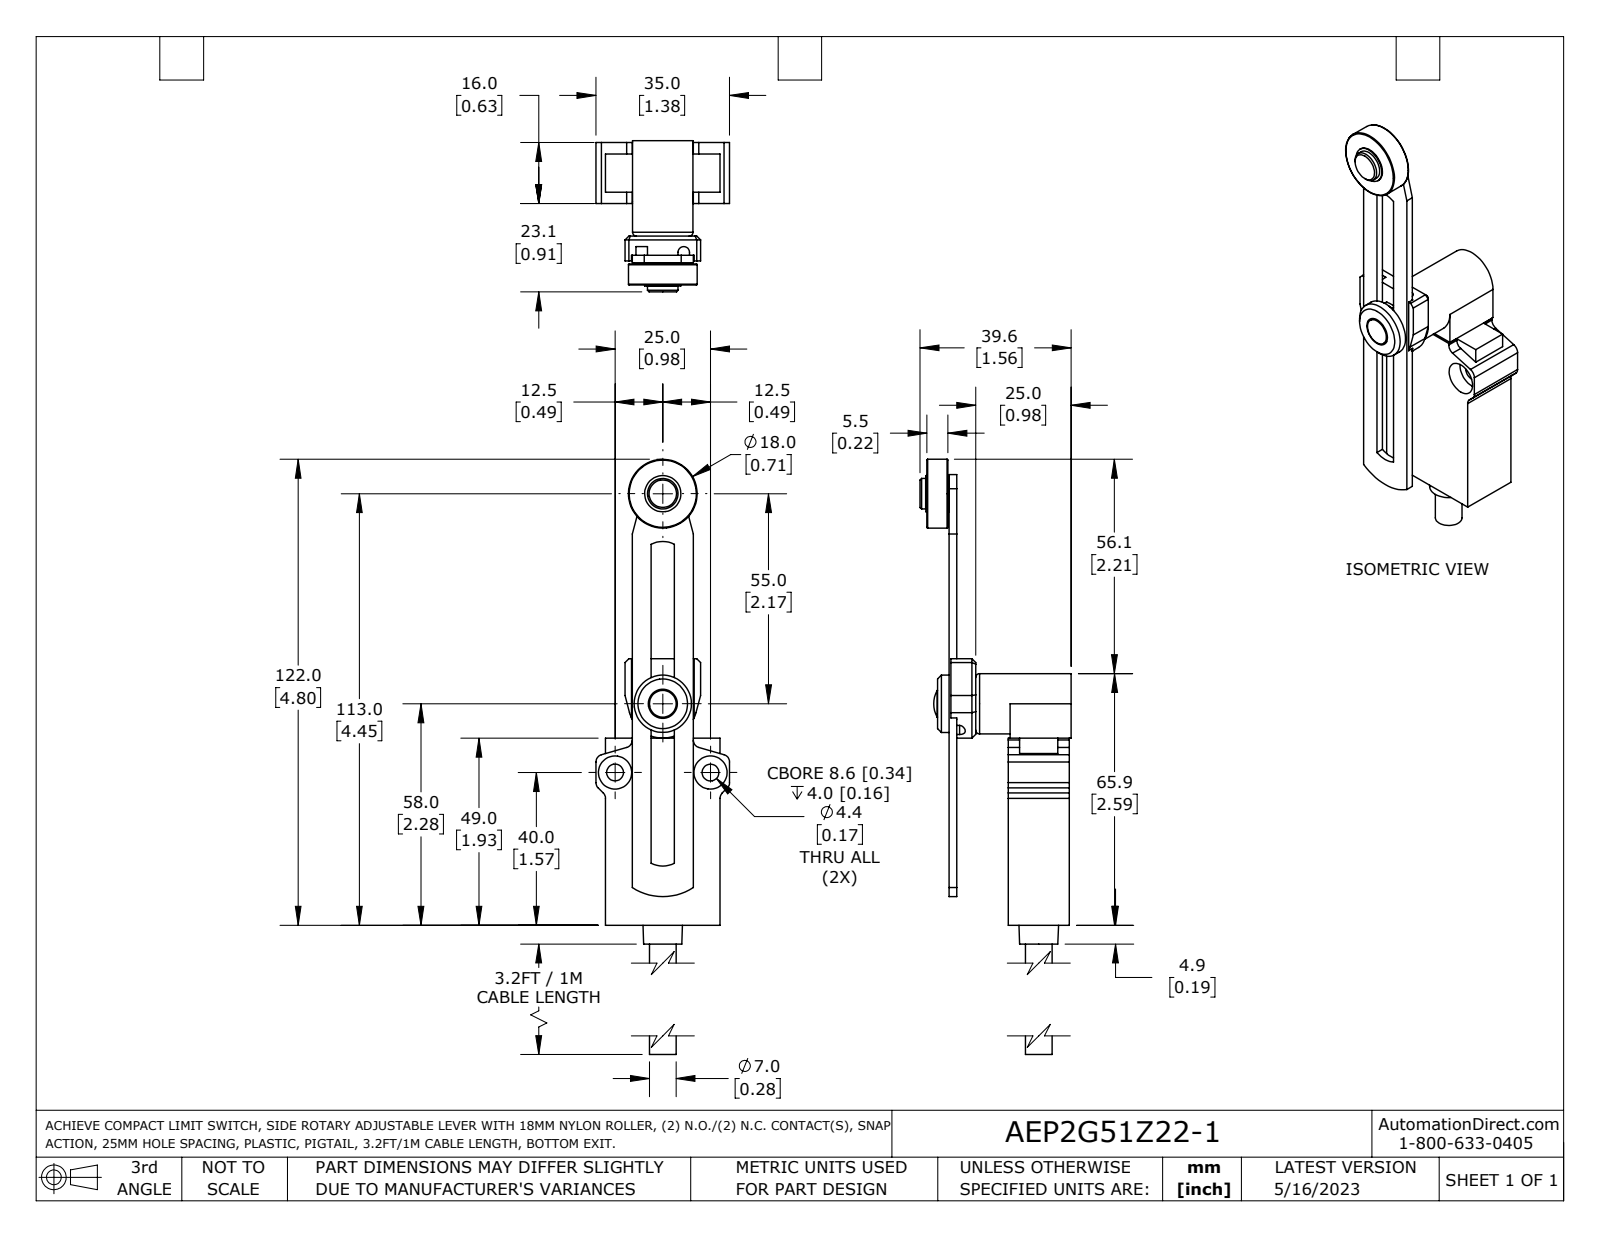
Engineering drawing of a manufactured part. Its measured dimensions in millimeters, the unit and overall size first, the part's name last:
Units: millimetres
Overall size (bounding box): 136.9 × 39.6 × 35
Round holes (diameter × count): ⌀4.4 ×2, ⌀8.7 ×2, ⌀5 ×1, ⌀7.6 ×1, ⌀11 ×1
Round bosses / shafts (diameter × count): ⌀7 ×2, ⌀18 ×1, ⌀15.8 ×1, ⌀15 ×1, ⌀9.5 ×1, ⌀8 ×1, ⌀6 ×1
Partial cylindrical surfaces — rounded edges, fillets, slot ends (radius × count): R2 ×8, R6.5 ×3, R1.5 ×1, R4.6 ×1, R5 ×1, R6.4 ×1, R9 ×1, R14.5 ×1
Main face-to-face distances: 16, 13.5, 15.5, 2, 31.5, 29.5, 30, 7, 23, 0.5
Hole centre spacings: 21.9, 25
Volume: 34 220 mm³ · Surface area: 13 990 mm²
Bodies: 1 solid, 151 faces (100 planar, 43 cylindrical, 8 other)
Part name (STEP PRODUCT): AEP2G51Z22-1
STEP written by: SolidWorks 2021 (AUTOMOTIVE_DESIGN)
